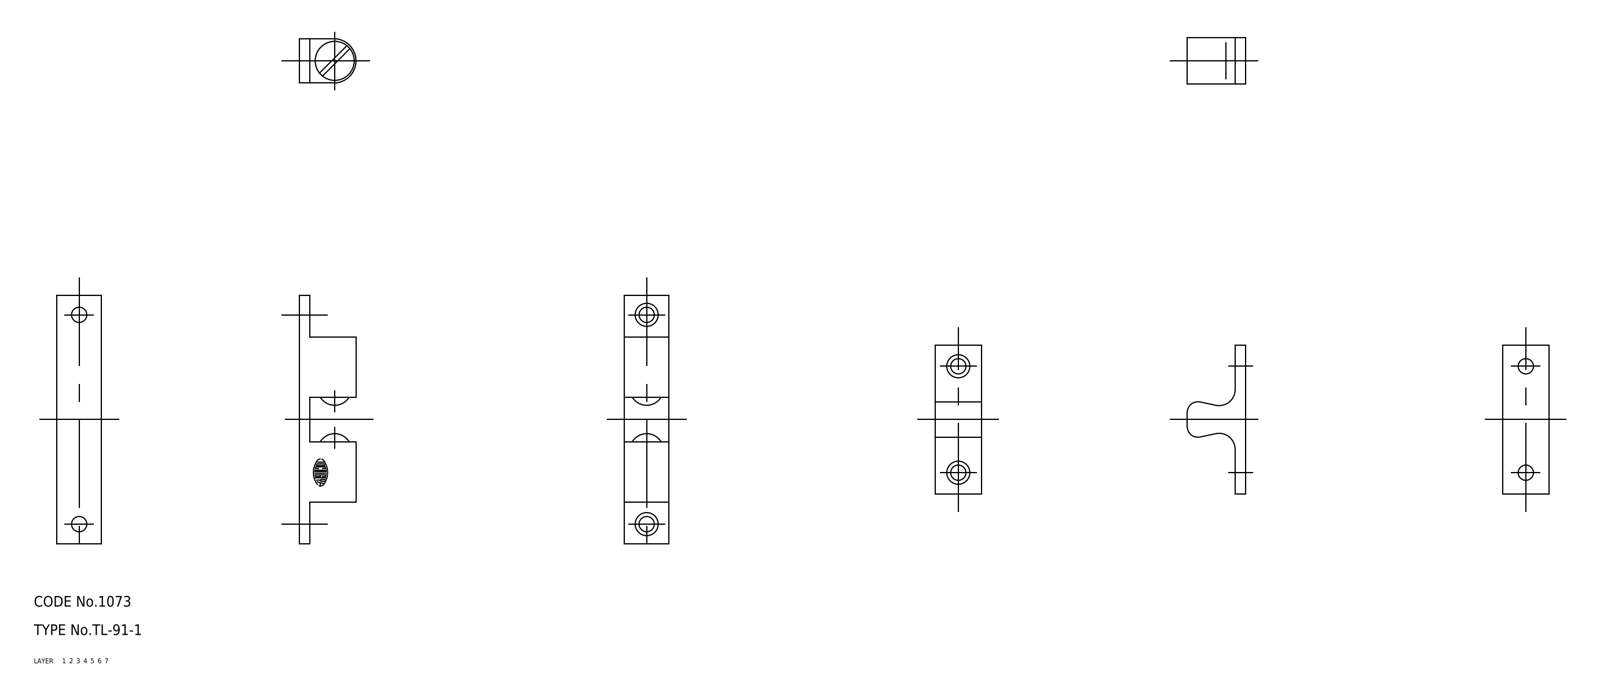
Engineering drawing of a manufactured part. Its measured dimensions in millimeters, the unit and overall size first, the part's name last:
Units: millimetres
Overall size (bounding box): 70 × 67.79 × 13
Volume: 9 622 mm³ · Surface area: 7 717 mm²
Bodies: 6 solids, 85 faces (0 planar, 0 cylindrical, 85 other)
Part name (STEP PRODUCT): screw; ball; keeper; housing (+1 more)
STEP written by: CADfix (AUTOMOTIVE_DESIGN)
